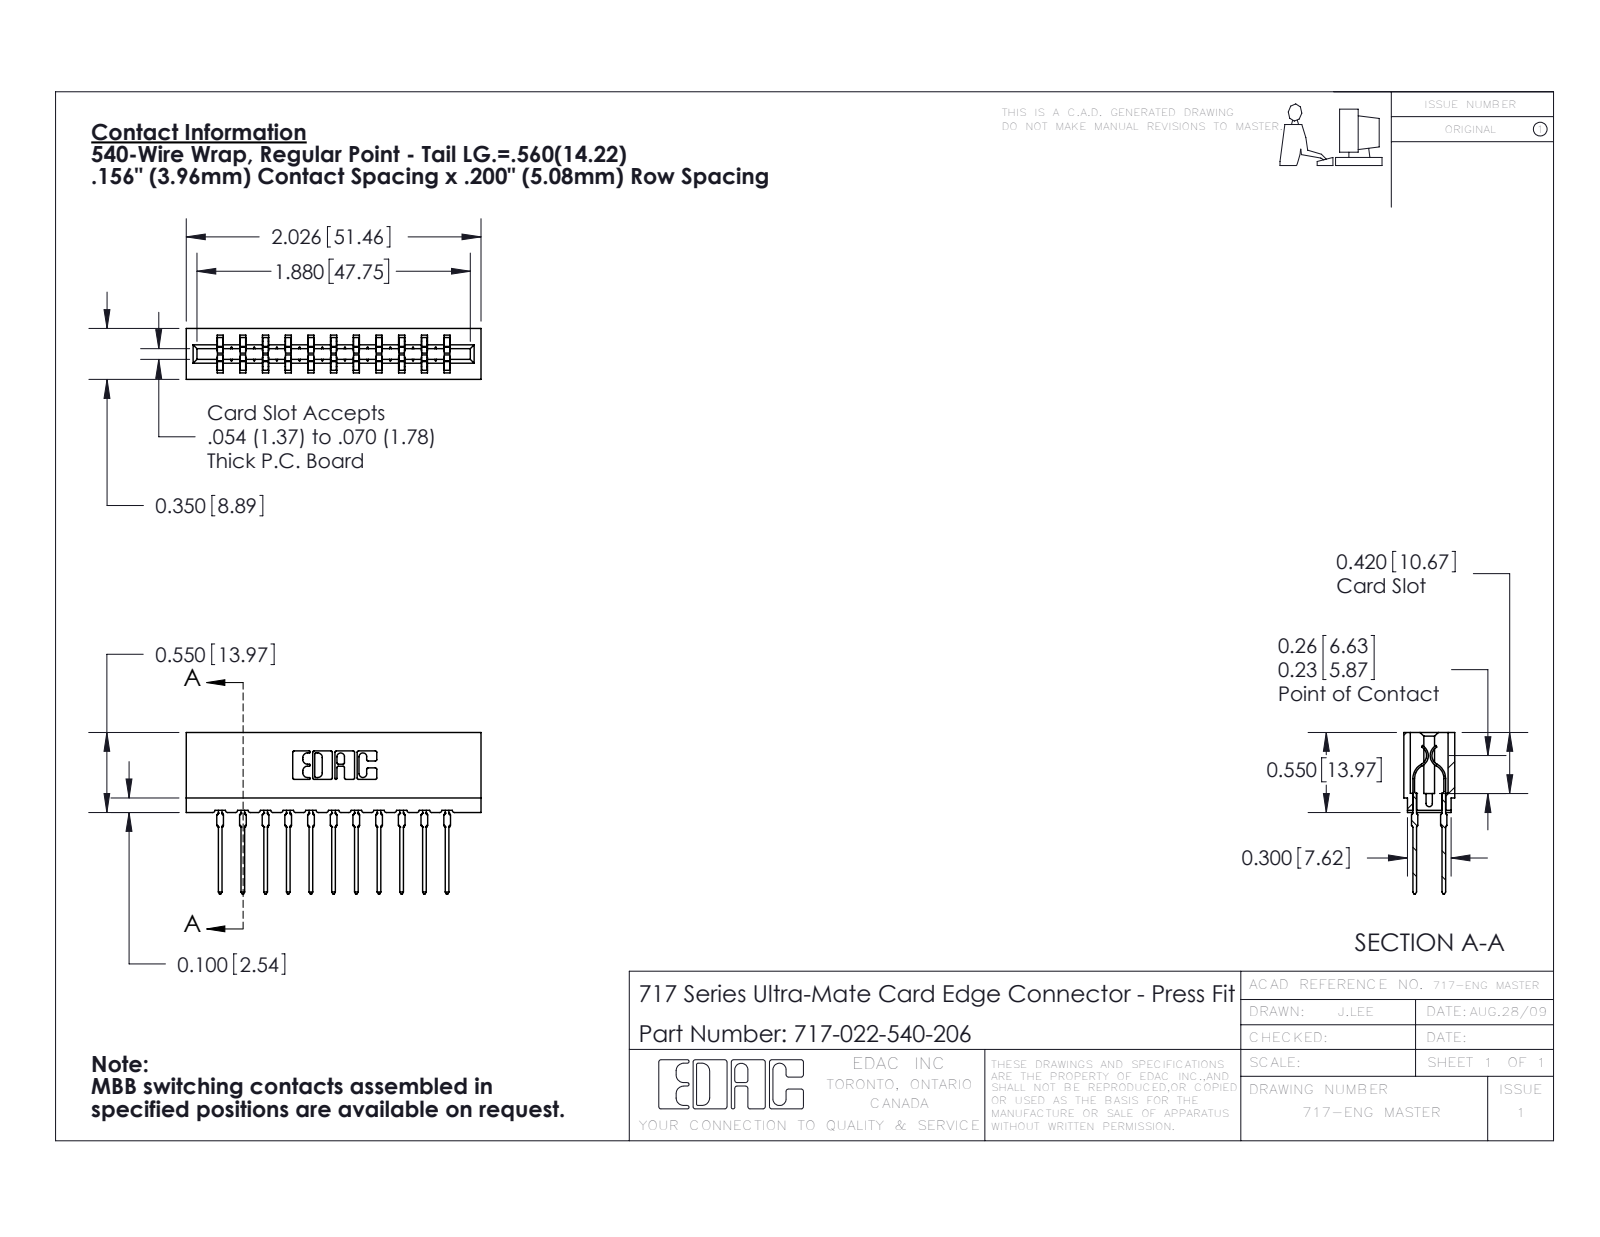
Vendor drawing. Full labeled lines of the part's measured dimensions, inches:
Part name (STEP PRODUCT): 745-292-001_540; 717-022-540-206; 717 Part_Insulator Option - 06
STEP written by: SolidWorks 2016 (CONFIG_CONTROL_DESIGN)
Units: inches
Bodies: 23 solids, 2074 faces (1077 planar, 425 cylindrical, 572 other)
Overall size (bounding box): 2.026 × 1.109 × 0.35
Volume: 0.284 in³ · Surface area: 10.83 in²
Partial cylindrical surfaces — rounded edges, fillets, slot ends (radius × count): R0.021 ×44, R0.01 ×22, R0.015 ×22, R0.005 ×8, R0.011 ×8, R0.007 ×6, R0.031 ×6, R0.026 ×3
Main face-to-face distances: 0.212, 0.156, 0.138, 0.468, 0.624, 0.35, 0.312, 0.198, 0.063, 0.287
